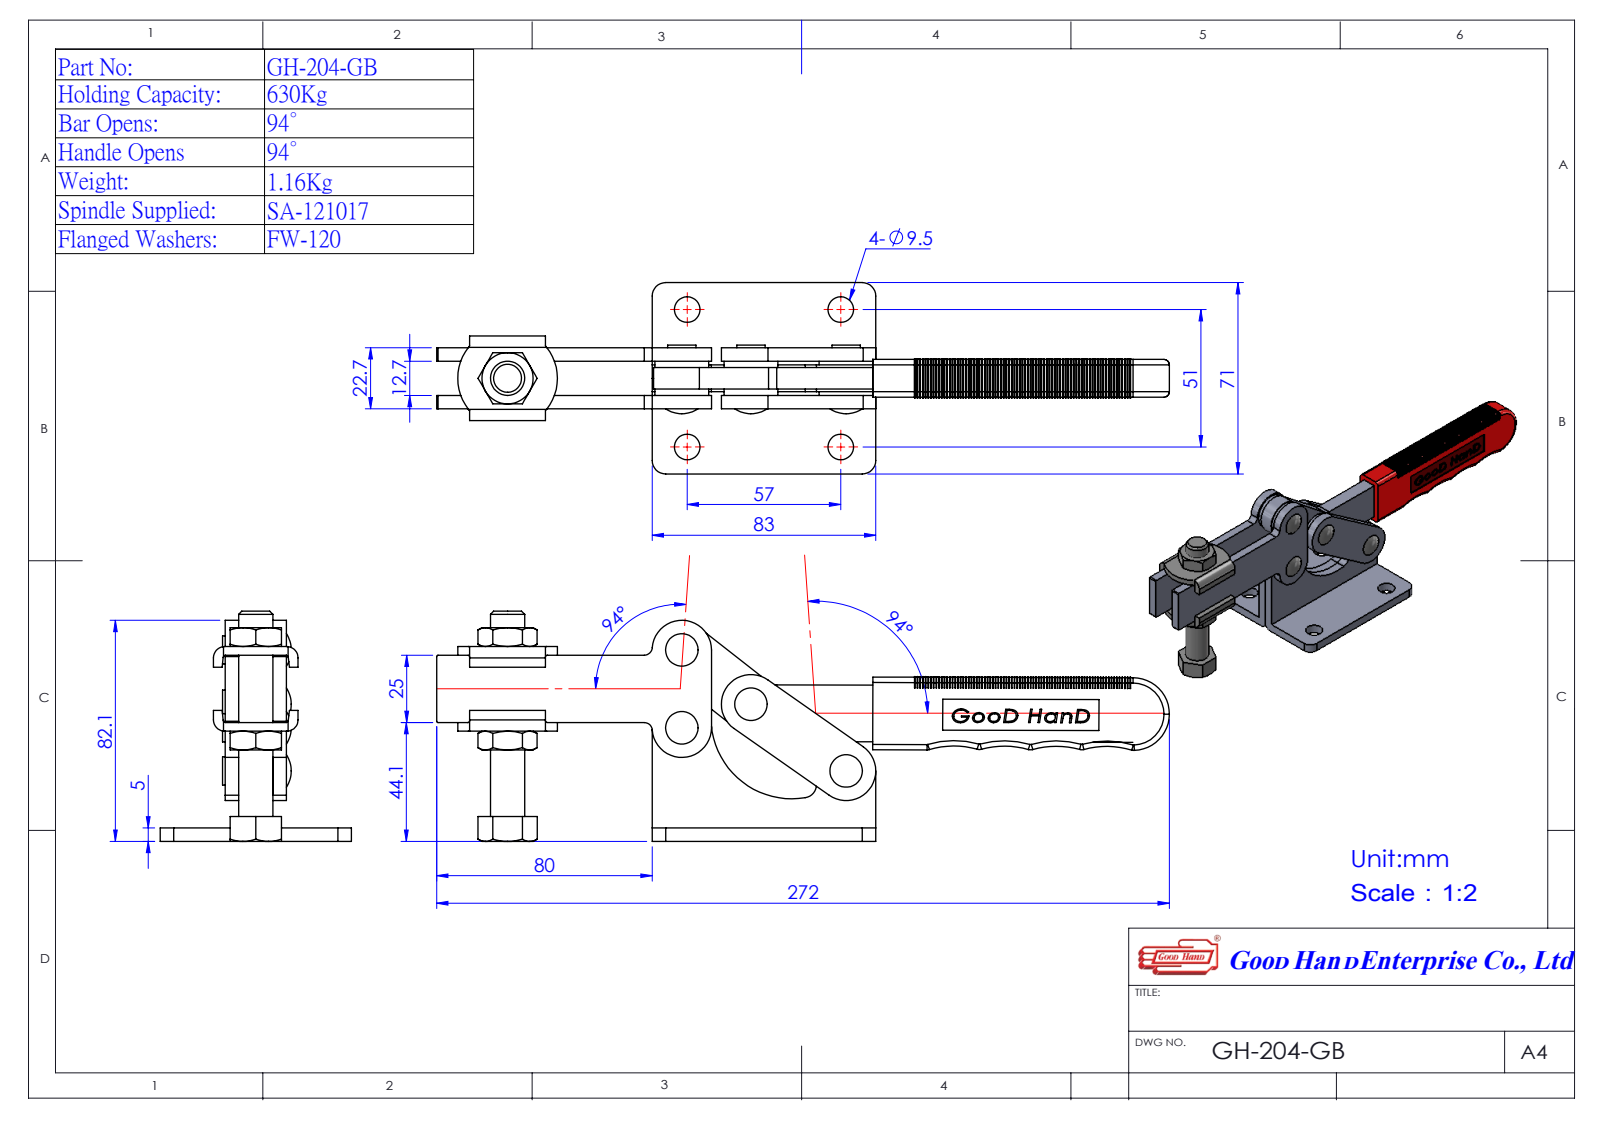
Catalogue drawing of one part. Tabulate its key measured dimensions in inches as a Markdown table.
| quantity | value |
| --- | --- |
| part name | Group3^GH-204-GB(簡化); Group5^GH-204-GB(簡化); GH-204-GB(簡化); Group4^GH-204-GB(簡化) (+2 more) |
| STEP written by | SolidWorks 2016 (AUTOMOTIVE_DESIGN) |
| units | inches |
| bodies | 5 solids, 284 faces (112 planar, 132 cylindrical, 40 other) |
| overall size | 10.709 × 4.301 × 2.795 |
| volume | 10.92 in³ |
| surface area | 106.1 in² |
| round holes (diameter × count) | 0.374 × 5, 0.315 × 4, 0.394 × 2, 0.512 × 1 |
| round bosses / shafts (diameter × count) | 0.787 × 4, 0.413 × 4, 0.374 × 2, 0.866 × 1, 0.5 × 1 |
| partial cylindrical surfaces (radius × count) | 0.118 × 7, 0.197 × 7, 0.039 × 4, 0.165 × 4, 1.26 × 4, 0.433 × 3, 0.02 × 2, 0.413 × 1 |
| main face-to-face distances | 0.197, 0.697, 0.171, 0.644, 0.722, 0.026, 0.526, 0.25, 0.079, 0.472 |
| hole center spacings | 2.008, 2.244, 2.811, 3.011, 4.972, 1.068, 1.138, 1.285 |
